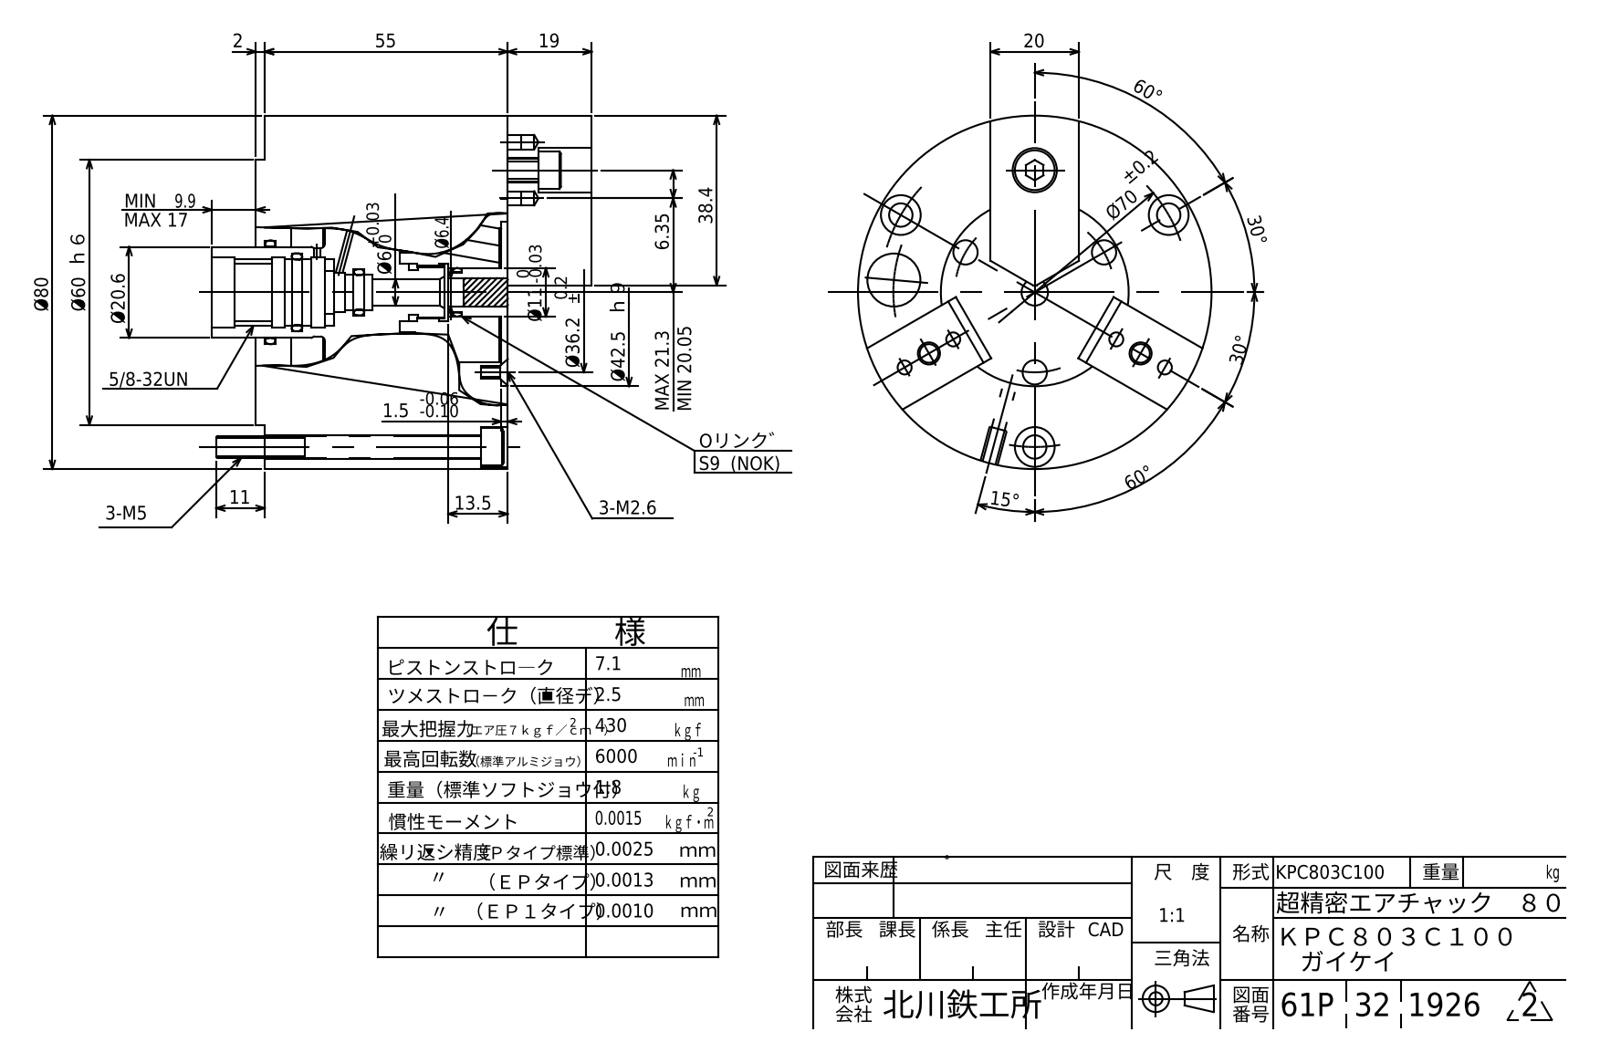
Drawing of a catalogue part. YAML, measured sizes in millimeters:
part_name: "KPC803C100"
step_written_by: "ST-DEVELOPER v16.7 (AUTOMOTIVE_DESIGN)"
units: millimeters
bodies: {solids: 1, faces: 507, planar: 344, cylindrical: 112, other: 51}
overall_size: [85.9, 80, 80]
volume: 309743
surface_area: 57492
round_holes:
  - {diameter: 5.5, count: 9}
  - {diameter: 3.3, count: 6}
  - {diameter: 4, count: 6}
  - {diameter: 4.5, count: 6}
  - {diameter: 8, count: 6}
  - {diameter: 9, count: 4}
  - {diameter: 2.1, count: 3}
  - {diameter: 5, count: 3}
  - {diameter: 10, count: 3}
  - {diameter: 6, count: 1}
  - {diameter: 6.4, count: 1}
  - {diameter: 7.96, count: 1}
round_bosses_or_shafts:
  - {diameter: 8.5, count: 6}
  - {diameter: 7, count: 6}
  - {diameter: 5, count: 3}
  - {diameter: 4.5, count: 3}
  - {diameter: 2.6, count: 3}
  - {diameter: 80, count: 1}
  - {diameter: 60, count: 1}
  - {diameter: 20.6, count: 1}
partial_cylinders:
  - {radius: 21.25, count: 1}
face_to_face_distances: [57, 2, 19, 55, 37, 76, 74, 20, 4.5, 18]
hole_center_spacings: [35, 60.62, 17.7, 18.12, 24.33, 46.76, 49.5, 51.48]
